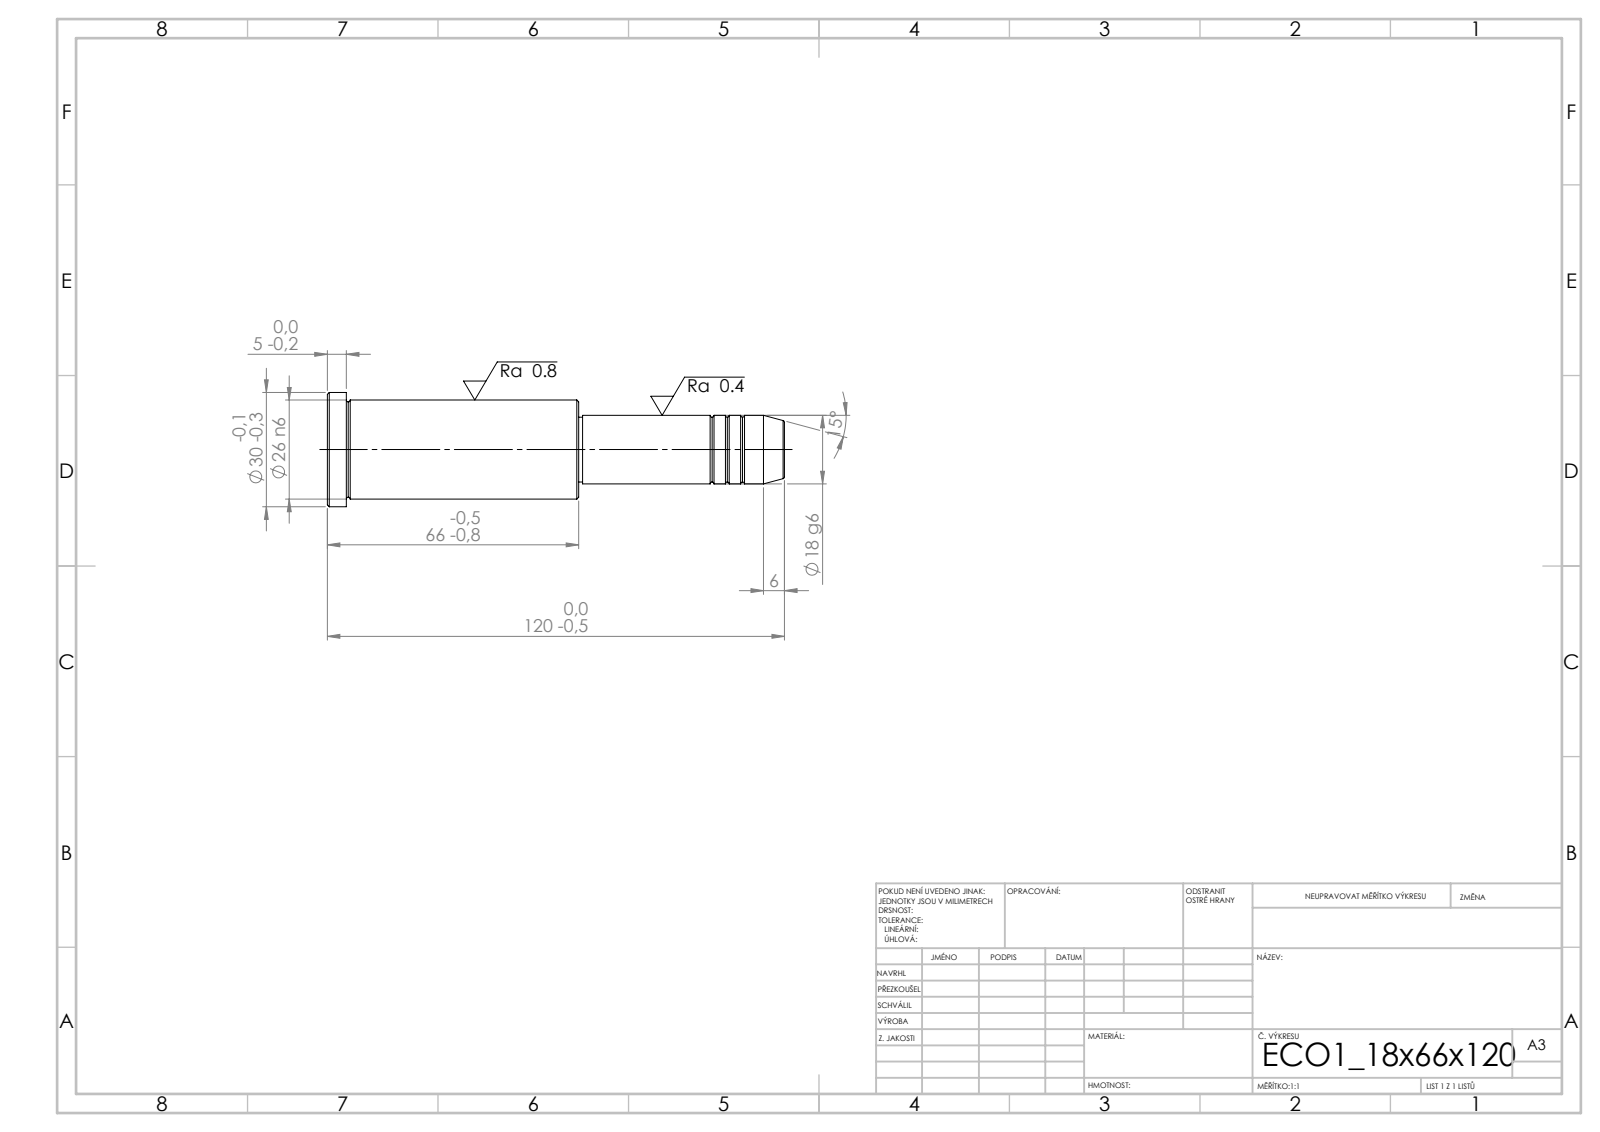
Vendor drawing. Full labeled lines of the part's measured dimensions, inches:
STEP written by: SolidWorks 2019 (CONFIG_CONTROL_DESIGN)
Units: inches
Bodies: 1 solid, 43 faces (5 planar, 14 cylindrical, 24 other)
Overall size (bounding box): 4.724 × 1.181 × 1.181
Volume: 3.008 in³ · Surface area: 15.43 in²
Round bosses / shafts (diameter × count): ⌀1.181 ×1, ⌀1.024 ×1, ⌀0.709 ×1, ⌀0.669 ×1
Main face-to-face distances: 2.598, 2.402, 0.197, 2.126, 4.528, 4.724, 2.087, 0.039, 2.441, 2.638
